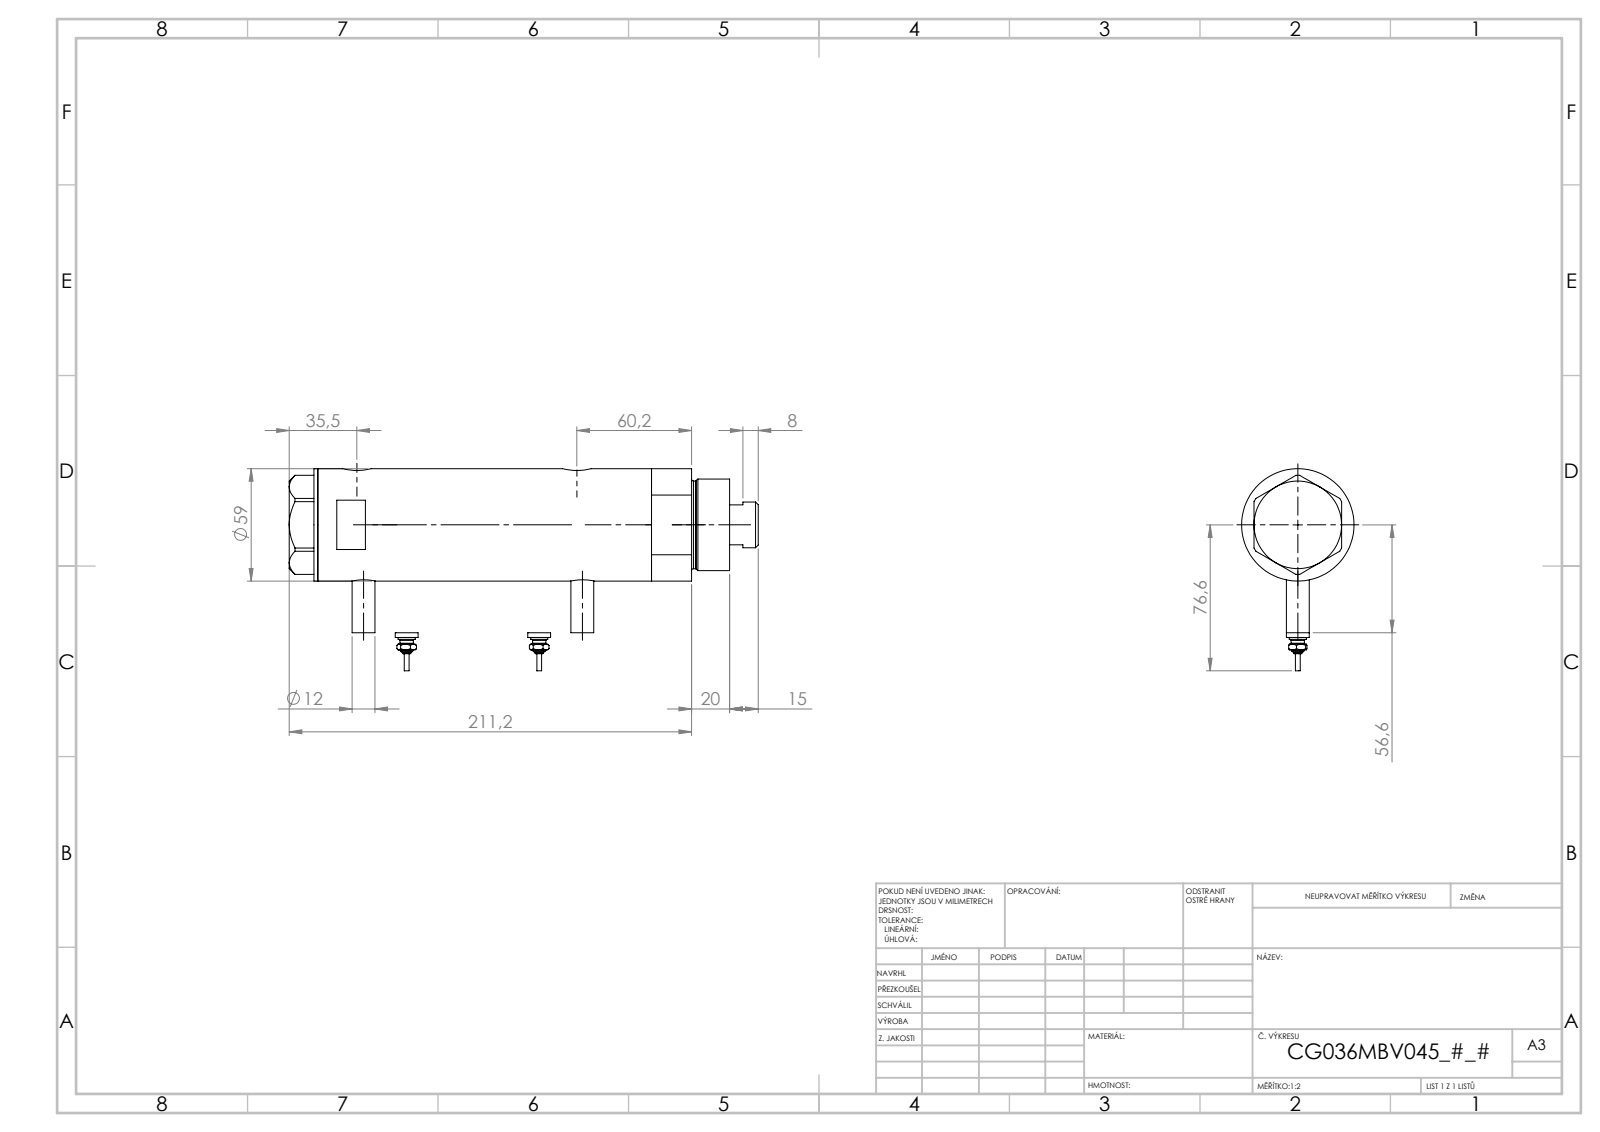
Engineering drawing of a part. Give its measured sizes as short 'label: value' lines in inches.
name: V270CG_VC; V270CG_BACK; Switch; V270CG_FRONT (+1 more)
written by: SolidWorks 2019 (CONFIG_CONTROL_DESIGN)
unit: in
bodies: 6 solids, 212 faces (79 planar, 69 cylindrical, 64 other)
size: 9.693 × 4.177 × 2.323
volume: 35.56 in³; area: 181.9 in²
holes: 2× ⌀0.383, 2× ⌀0.492, 2× ⌀0.591, 1× ⌀0.335, 1× ⌀0.984, 1× ⌀1.043, 1× ⌀1.417, 1× ⌀1.575, 1× ⌀2.047
bosses: 4× ⌀0.472, 2× ⌀0.354, 2× ⌀0.276, 2× ⌀0.177, 2× ⌀0.098, 1× ⌀2.323, 1× ⌀1.89, 1× ⌀1.811
face distances: 5.402, 0.925, 4.476, 0.591, 1.516, 5.992, 0.079, 9.102, 8.512, 7.587
hole spacings: 0.114, 0.138, 4.409, 4.524, 4.547, 4.661
